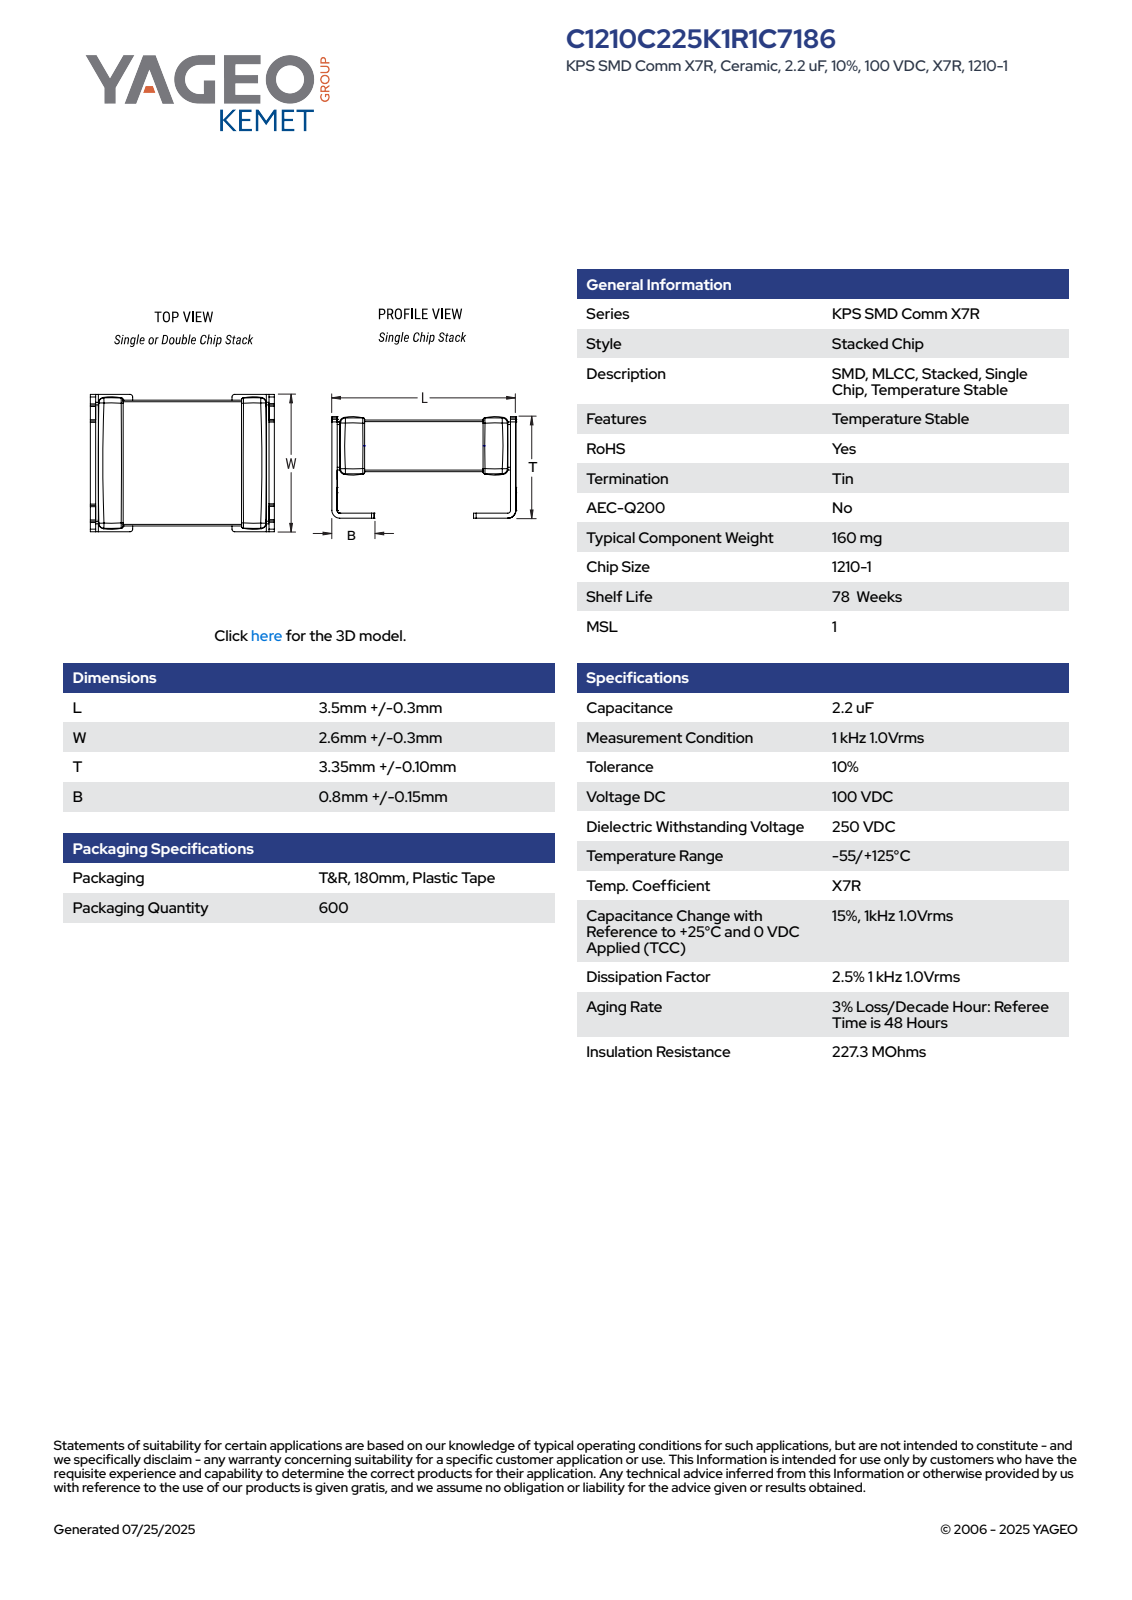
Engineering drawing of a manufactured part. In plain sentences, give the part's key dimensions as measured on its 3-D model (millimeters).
The part is named "CCSS_S1_1210-1_L3.8W2.9T3.45B0.95". Its 3-D file was written by "SolidWorks 2021 (AUTOMOTIVE_DESIGN)". It is 4 solids with 169 faces: 105 planar, 52 cylindrical and 12 other. Overall it measures 3.8 by 3.45 by 2.9 millimeters. Its volume is 33 cubic millimeters and its surface area 77 square millimeters. The main face-to-face distances are 2.9, 3.8, 2.85, 2.95, 3, 0.45, 3.45, 3.35, 0.35, 3.4.
